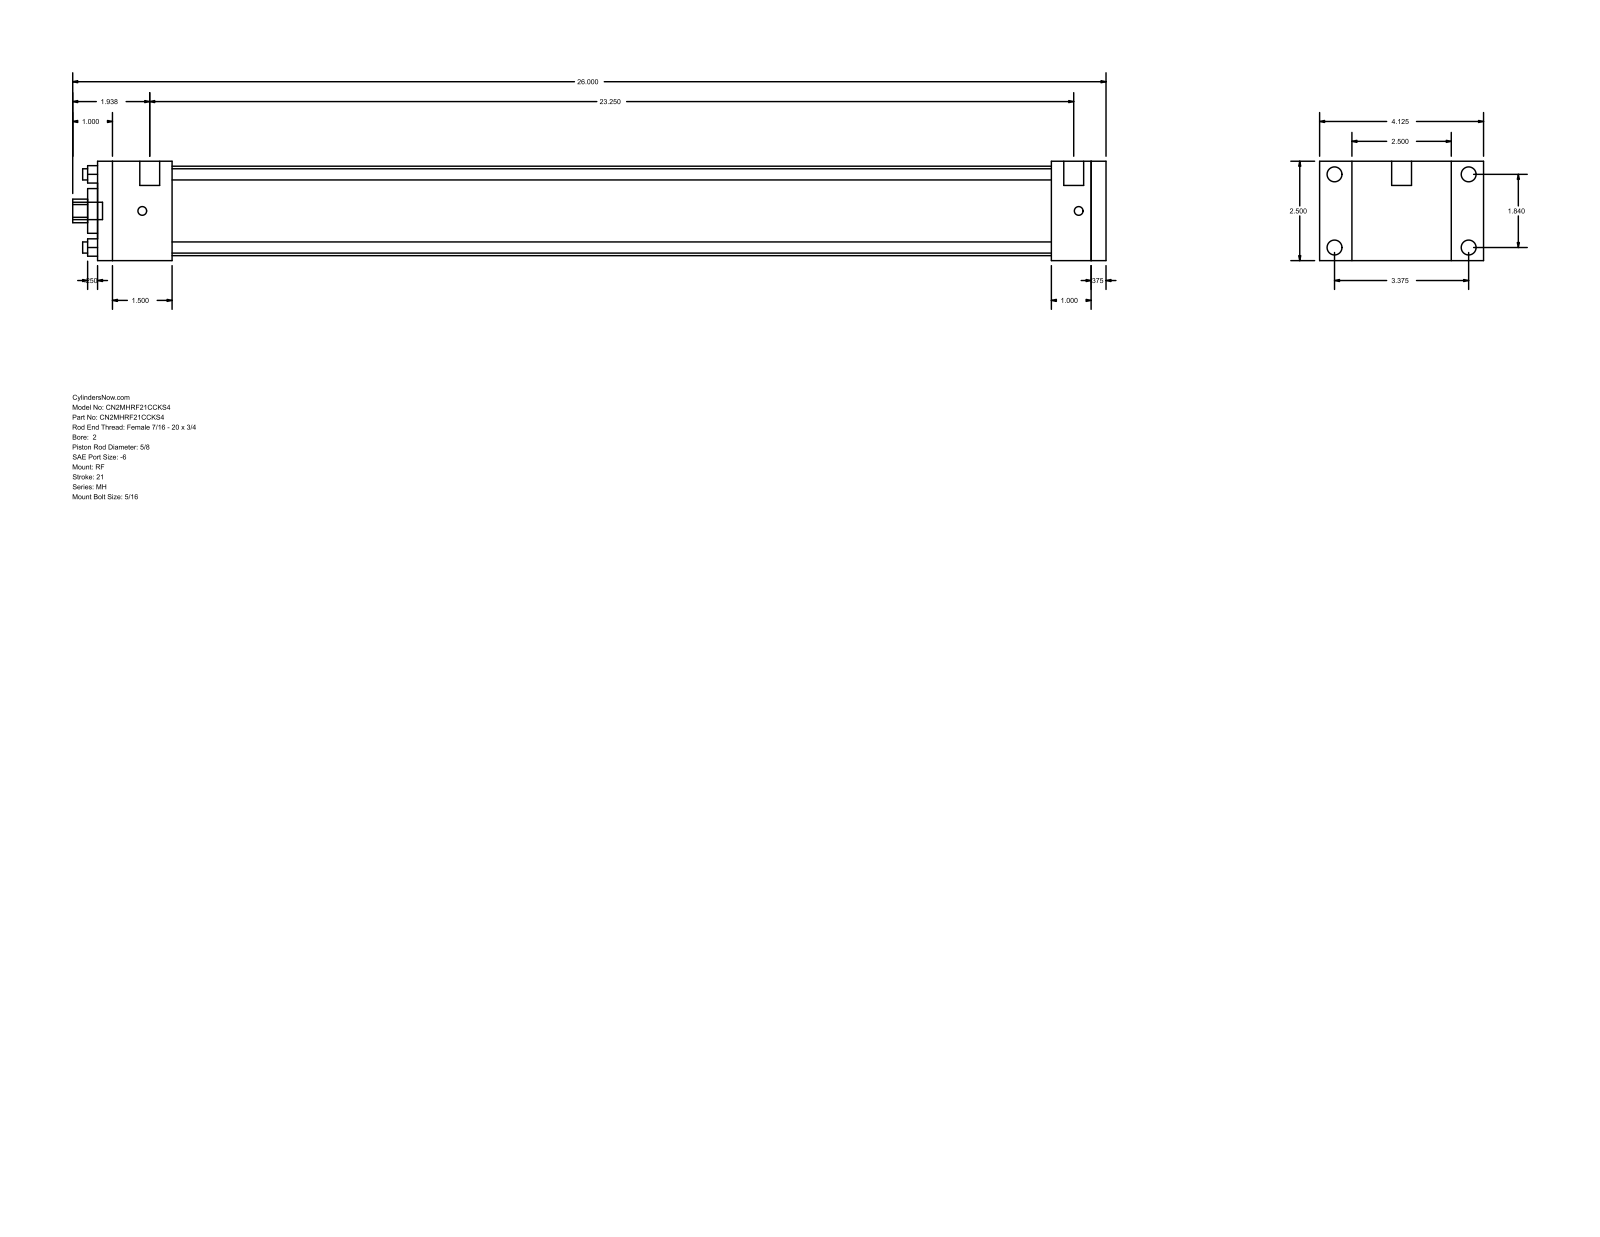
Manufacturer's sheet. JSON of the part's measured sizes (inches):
{"part_name": "MH_RF__0200_0.625", "step_written_by": "GSSL Pune (CONFIG_CONTROL_DESIGN)", "units": "inches", "bodies": {"solids": 0, "faces": 92, "planar": 64, "cylindrical": 28, "other": 0}, "overall_size": [26, 4.125, 2.5], "round_holes": [[0.281, 4], [0.625, 1], [1.125, 1], [2.25, 1]], "round_bosses_or_shafts": [[0.375, 4], [0.219, 4], [0.5, 2], [0.437, 1]], "partial_cylinders_radius": [[0.297, 1]], "face_to_face_distances": [2.5, 25.375, 0.375, 25, 1, 1.875, 24, 22.125, 23.125, 23.5], "hole_center_spacings": [1.301, 1.84, 2.602]}
